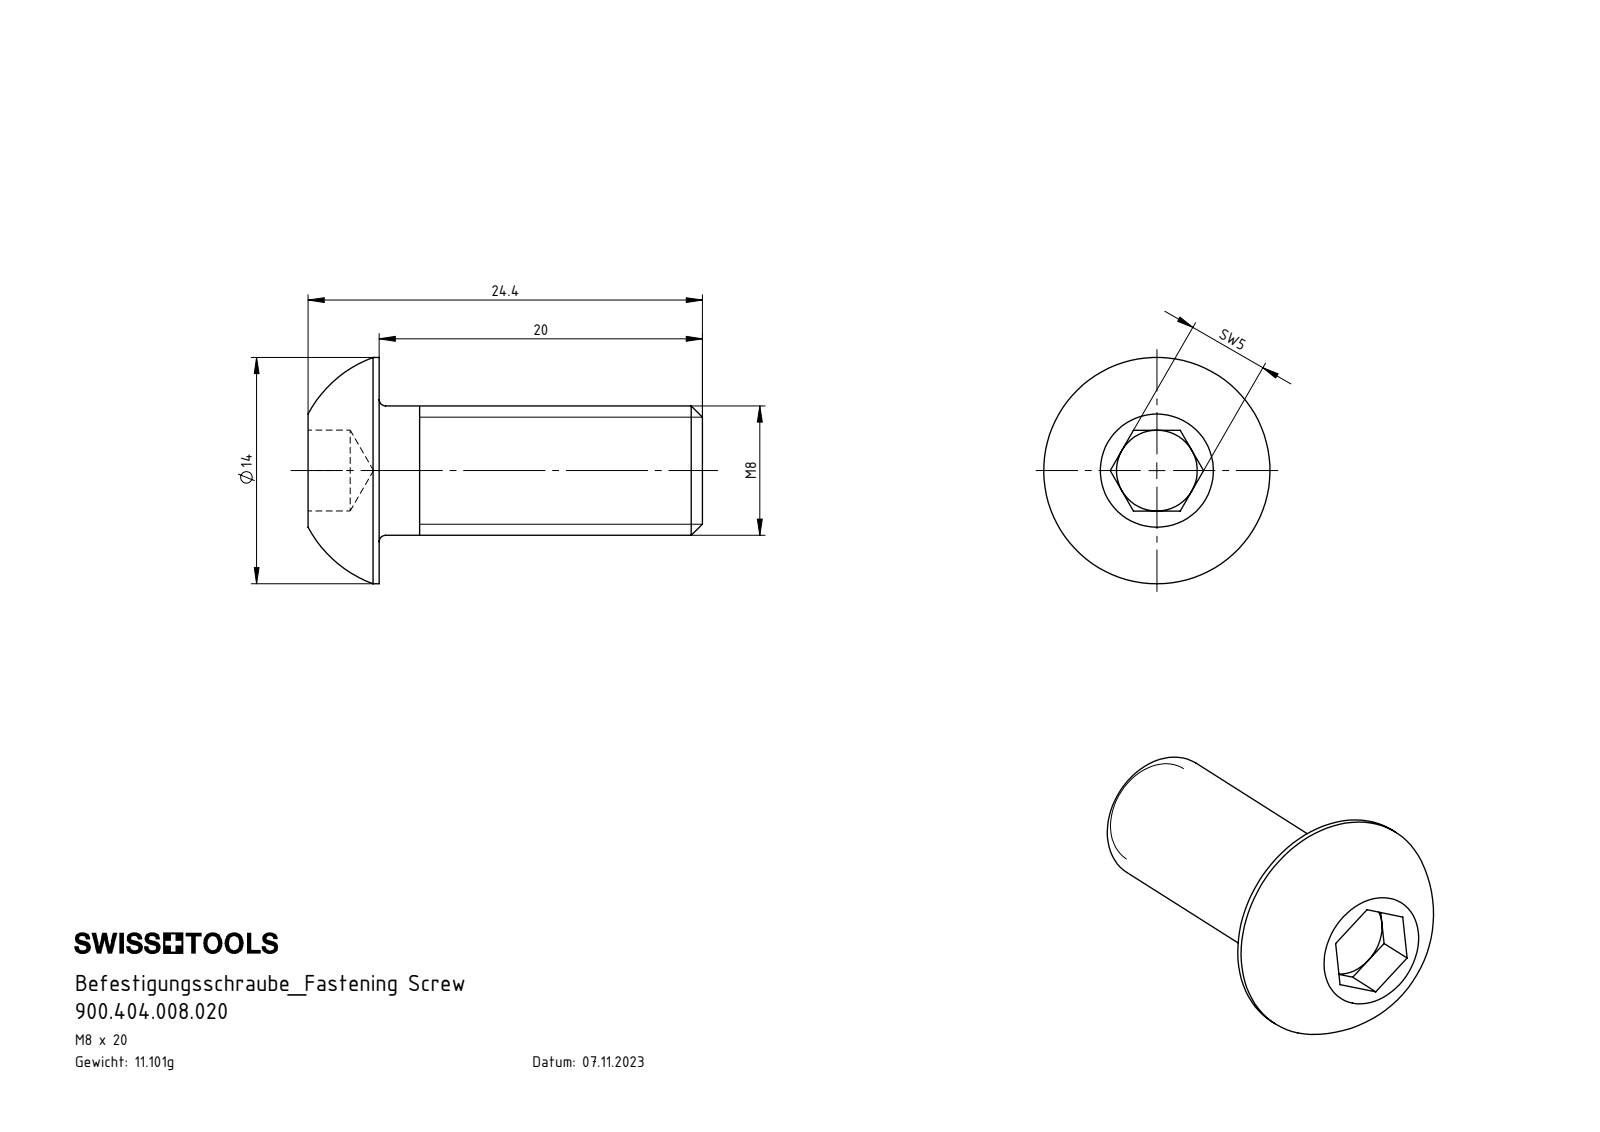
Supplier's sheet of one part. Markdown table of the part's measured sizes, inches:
| quantity | value |
| --- | --- |
| part name | 900.404.008.020 |
| STEP written by | SolidWorks 2022 (AUTOMOTIVE_DESIGN) |
| units | inches |
| bodies | 1 solid, 27 faces (15 planar, 4 cylindrical, 8 other) |
| overall size | 0.961 × 0.551 × 0.551 |
| volume | 0.086 in³ |
| surface area | 1.45 in² |
| round bosses / shafts (diameter × count) | 0.551 × 1, 0.315 × 1 |
| main face-to-face distances | 0.787, 0.197, 0.173, 0.961, 0.102, 0.071, 0.858 |
